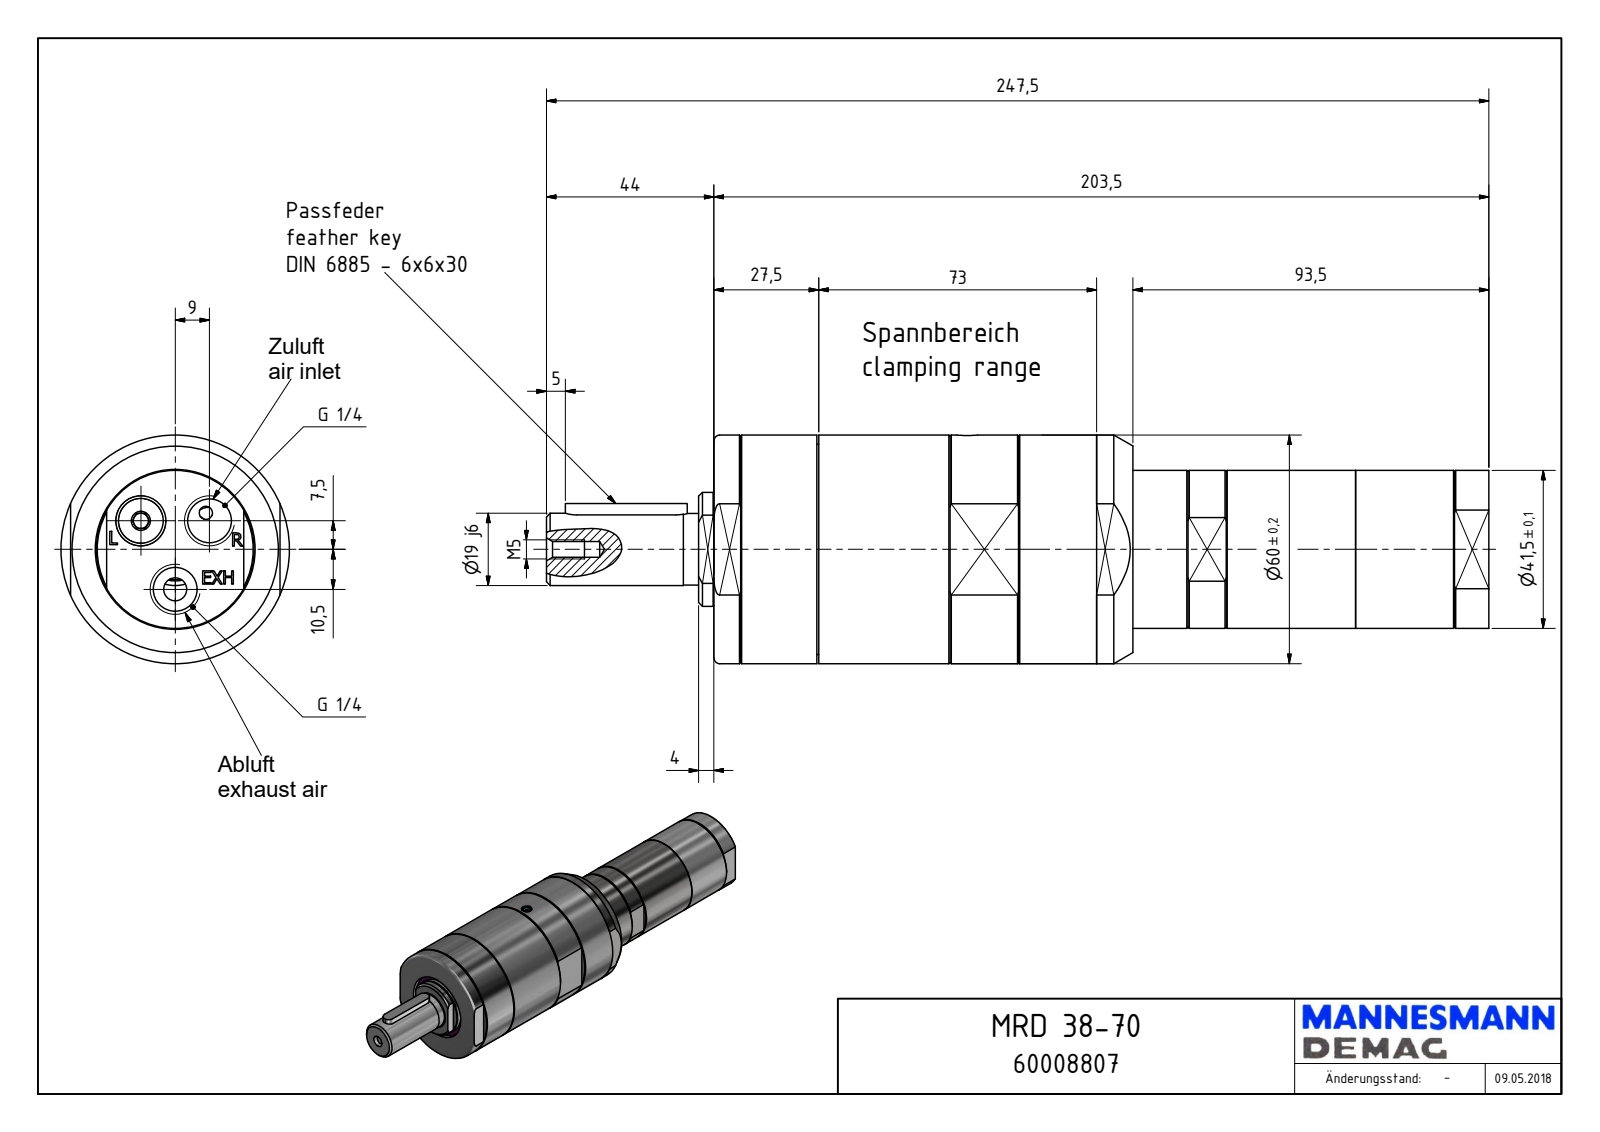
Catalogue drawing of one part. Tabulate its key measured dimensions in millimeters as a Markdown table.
| quantity | value |
| --- | --- |
| part name | MRD 38-70_60008807 |
| STEP written by | Autodesk Inventor 2018 (AUTOMOTIVE_DESIGN) |
| units | millimeters |
| bodies | 1 solid, 501 faces (220 planar, 231 cylindrical, 50 other) |
| overall size | 247.5 × 60 × 60 |
| volume | 442 681 mm³ |
| surface area | 48 564 mm² |
| round holes (diameter × count) | 11.45 × 3, 4 × 2, 1.55 × 1, 4.13 × 1, 5.5 × 1, 35 × 1, 42 × 1, 55.38 × 1, 57 × 1 |
| round bosses / shafts (diameter × count) | 60 × 1, 55.18 × 1, 54.53 × 1, 41.5 × 1, 39.5 × 1, 29.95 × 1, 19 × 1, 18.8 × 1 |
| partial cylindrical surfaces (radius × count) | 11.68 × 94, 3 × 2, 24.71 × 1, 24.96 × 1 |
| main face-to-face distances | 93.5, 55, 203.5, 110, 15, 1, 9.5, 4, 27.5, 82.5 |
| hole center spacings | 11.72, 20.12, 10.5, 18 |
